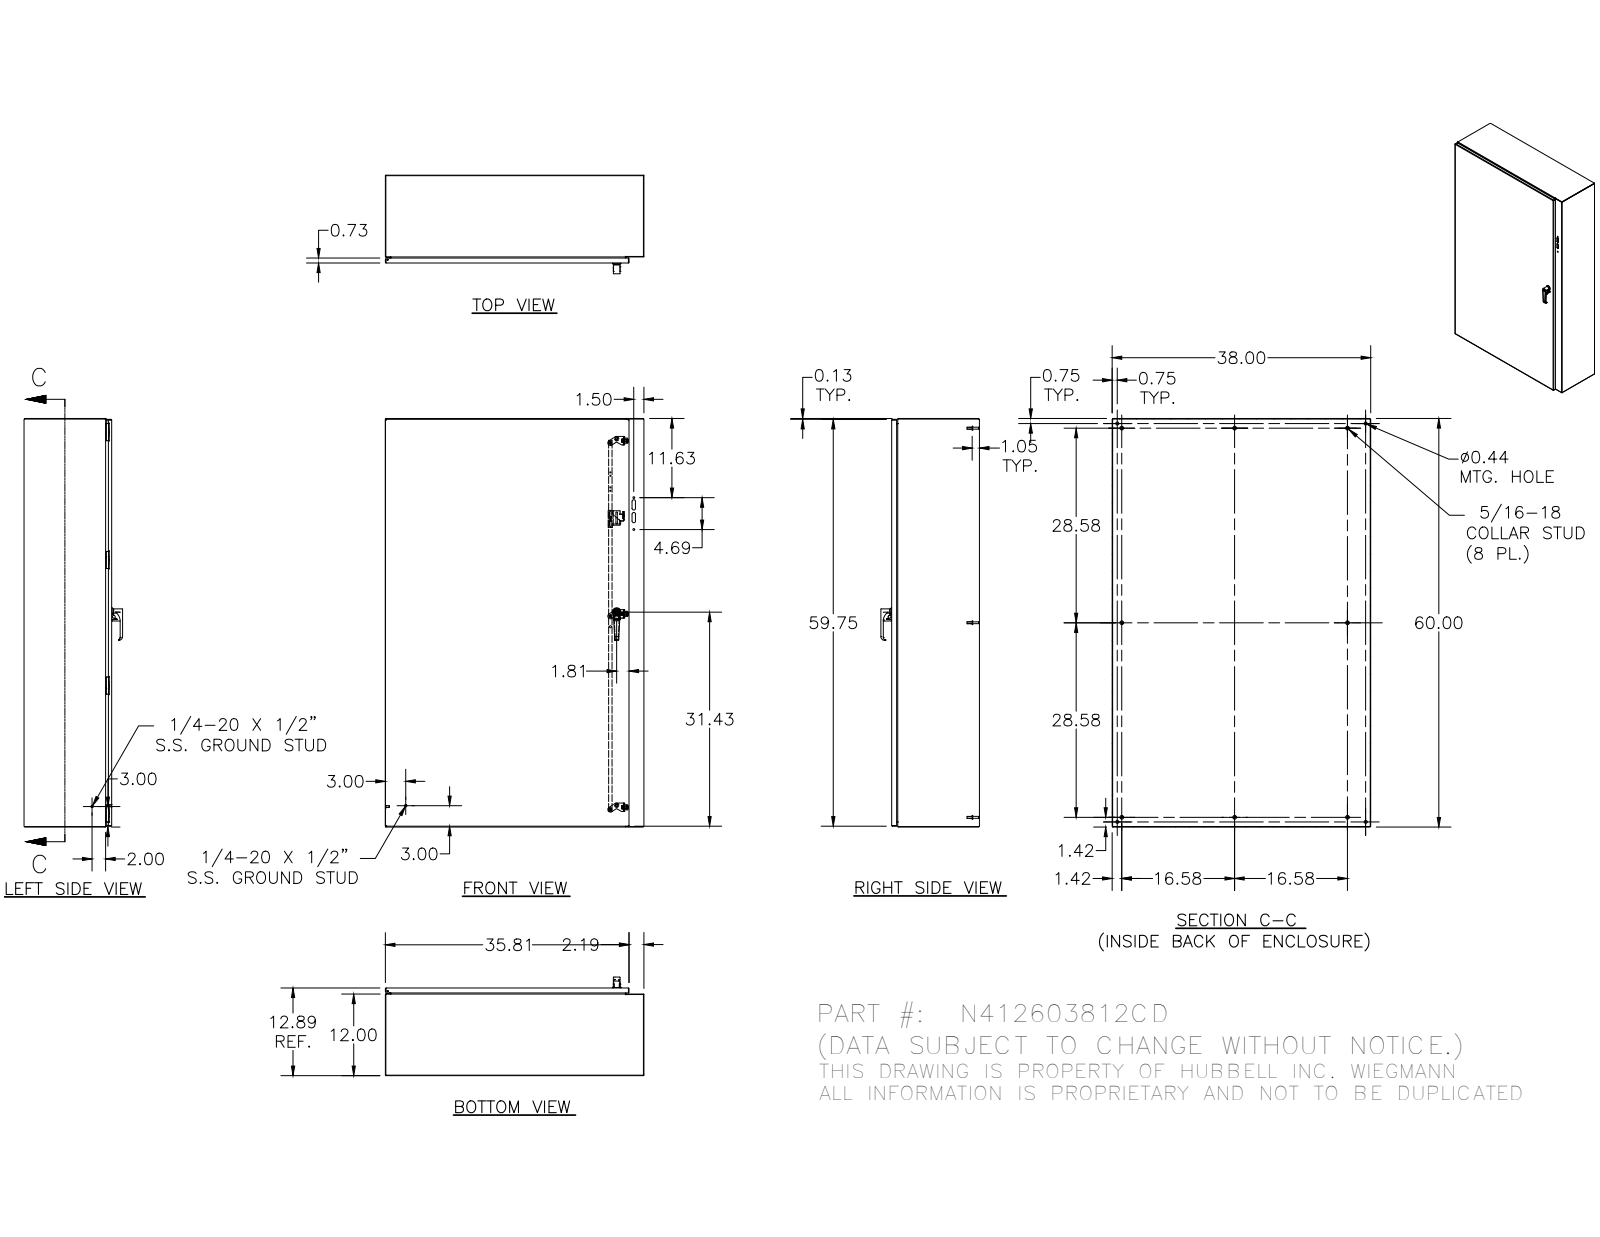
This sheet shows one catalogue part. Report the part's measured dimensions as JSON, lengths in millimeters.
{"part_name": "N412603812CD", "step_written_by": "SolidWorks 2019 (AUTOMOTIVE_DESIGN)", "units": "millimeters", "bodies": {"solids": 92, "faces": 3067, "planar": 1140, "cylindrical": 1136, "other": 791}, "overall_size": [1524, 965.2, 368.6], "volume_mm3": 9008000, "surface_area_mm2": 9530000, "round_holes": [[4.8, 9], [2.4, 8], [3.9, 8], [4.2, 8], [4.4, 8], [3.7, 6], [4, 6], [8.1, 4], [11.1, 4], [5, 3], [5.4, 3], [5.6, 3]], "round_bosses_or_shafts": [[6.4, 20], [7.6, 14], [14.3, 8], [9.1, 8], [8.1, 8], [6.5, 8], [4.2, 8], [3.3, 8]], "partial_cylinders_radius": [[1.3, 50], [3.2, 45], [0.5, 38], [0.4, 34], [0.3, 30], [0.6, 24], [0.8, 22], [0.8, 16]], "face_to_face_distances": [1.9, 326.2, 324.3, 328.1, 963.3, 1522.1, 961.4, 965.2, 302.9, 23.3], "hole_center_spacings": [476.9, 945.5, 12.7, 655, 716.6, 1371.6, 1422.4, 16.8]}
